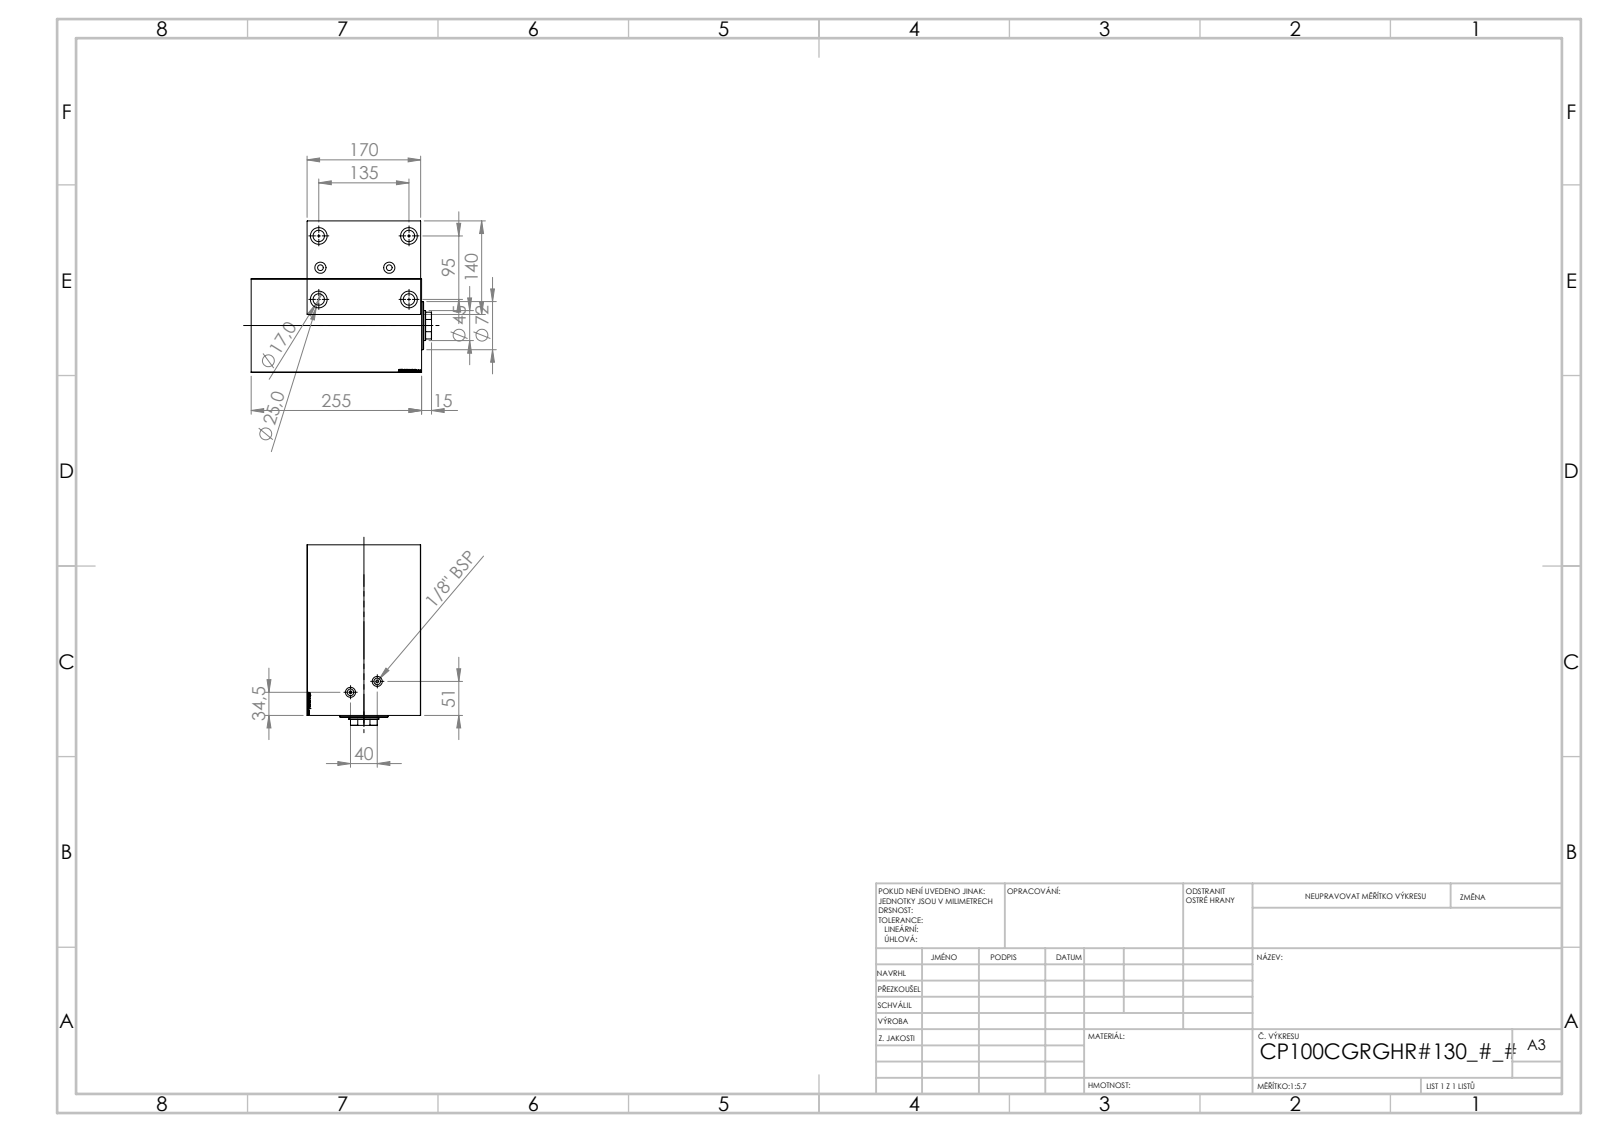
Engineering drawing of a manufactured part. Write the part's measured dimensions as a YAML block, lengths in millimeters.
part_name: "V450CP_C; V450CP_B_VCP; V450CP_VC_B"
step_written_by: "SolidWorks 2019 (CONFIG_CONTROL_DESIGN)"
units: millimeters
bodies: {solids: 3, faces: 883, planar: 413, cylindrical: 72, other: 398}
overall_size: [270, 170, 140]
volume: 4964000
surface_area: 448397
round_holes:
  - {diameter: 17, count: 4}
  - {diameter: 25, count: 4}
  - {diameter: 4, count: 2}
  - {diameter: 8.5, count: 2}
  - {diameter: 9.73, count: 2}
  - {diameter: 15, count: 2}
  - {diameter: 16.66, count: 2}
  - {diameter: 31.5, count: 1}
  - {diameter: 45, count: 1}
  - {diameter: 48.5, count: 1}
  - {diameter: 49.5, count: 1}
  - {diameter: 100, count: 1}
round_bosses_or_shafts:
  - {diameter: 72, count: 1}
partial_cylinders:
  - {radius: 22, count: 1}
face_to_face_distances: [140, 170, 255, 26, 229, 186, 160, 69, 56, 30]
hole_center_spacings: [82.54, 47.57, 55.92, 95, 115.7, 135, 140.76, 165.08]
